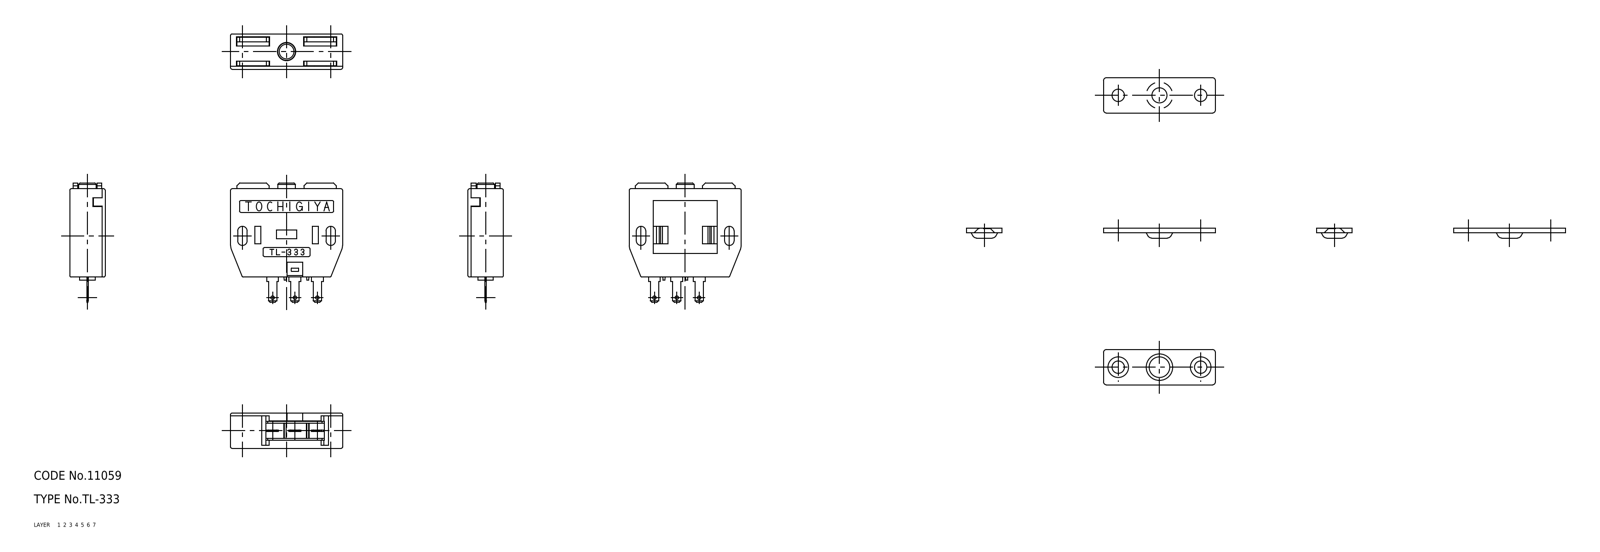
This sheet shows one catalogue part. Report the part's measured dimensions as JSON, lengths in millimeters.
{"part_name": "67118660; 67118673; 67118686; 67118699", "step_written_by": "CADfix (AUTOMOTIVE_DESIGN)", "units": "millimeters", "bodies": {"solids": 4, "faces": 250, "planar": 0, "cylindrical": 0, "other": 250}, "overall_size": [49, 38, 12], "volume_mm3": 11803, "surface_area_mm2": 10515}
